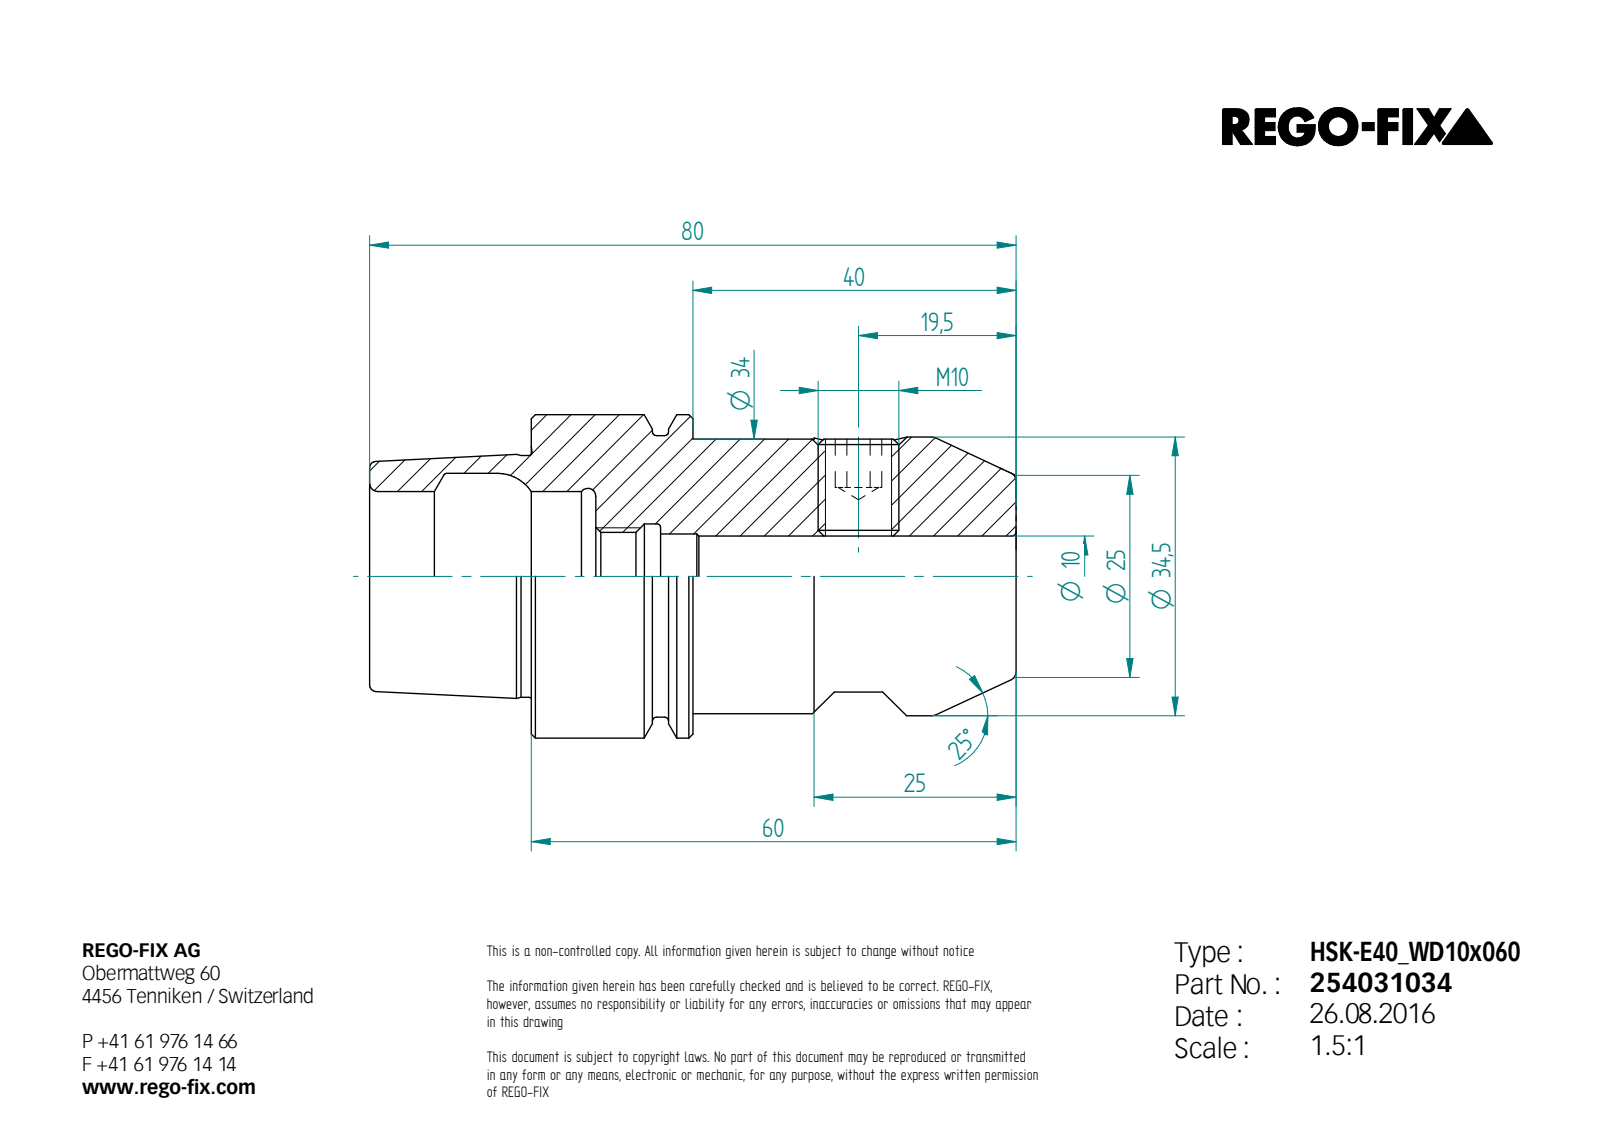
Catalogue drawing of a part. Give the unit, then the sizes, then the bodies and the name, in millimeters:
Units: millimetres
Overall size (bounding box): 80 × 40 × 40
Round holes (diameter × count): ⌀8.38 ×1, ⌀10 ×1, ⌀10.5 ×1, ⌀10.92 ×1, ⌀13 ×1, ⌀21 ×1, ⌀25.5 ×1
Round bosses / shafts (diameter × count): ⌀40 ×1, ⌀34.8 ×1, ⌀34.5 ×1, ⌀34 ×1, ⌀29.91 ×1, ⌀10 ×1
Main face-to-face distances: 20, 40, 60, 12, 8, 52, 28, 80, 5, 35
Volume: 60 178 mm³ · Surface area: 17 061 mm²
Bodies: 3 solids, 76 faces (28 planar, 17 cylindrical, 31 other)
STEP written by: Unknown (AUTOMOTIVE_DESIGN)
